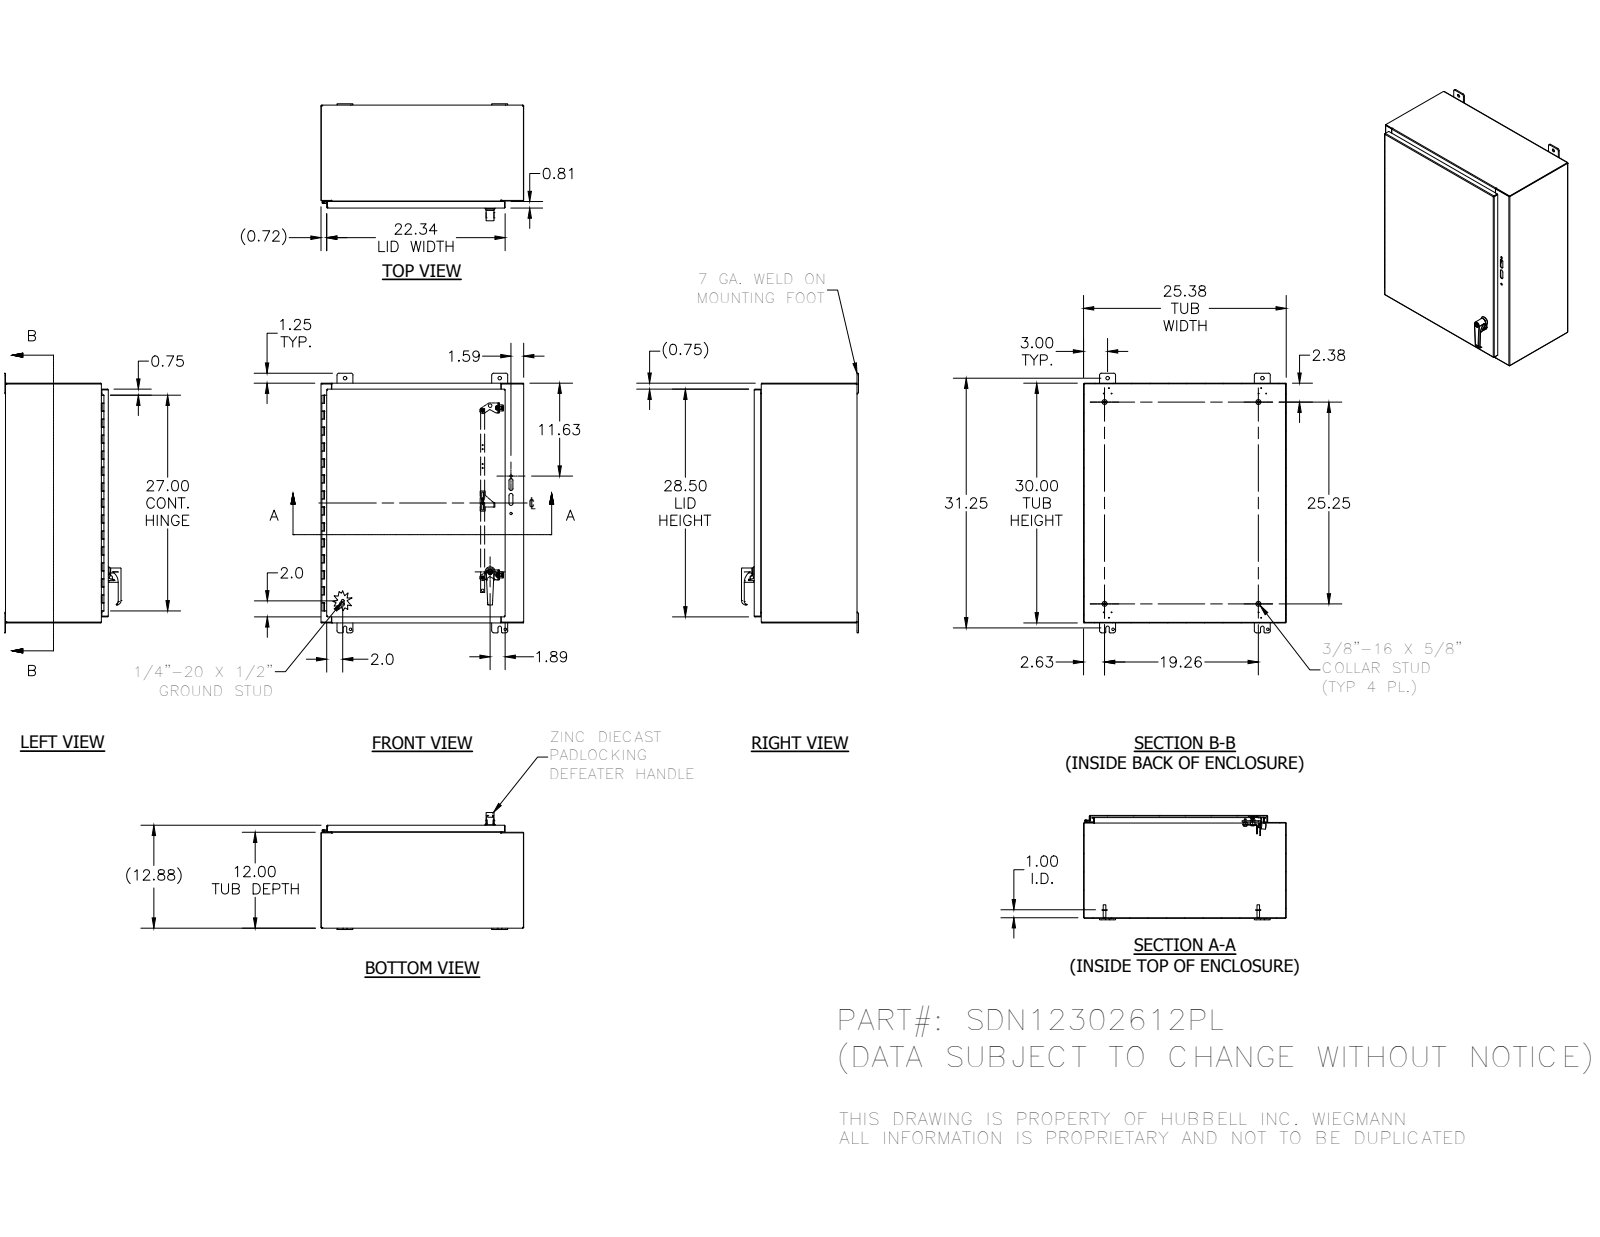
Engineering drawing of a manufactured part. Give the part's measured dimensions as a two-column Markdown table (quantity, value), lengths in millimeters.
| quantity | value |
| --- | --- |
| part name | SDN12302612PL; SDN12302612PLBKP; 388116; 34840 (+8 more) |
| STEP written by | Autodesk Inventor 2012 (AUTOMOTIVE_DESIGN) |
| units | millimeters |
| bodies | 49 solids, 1618 faces (836 planar, 557 cylindrical, 225 other) |
| overall size | 825.5 × 644.7 × 372.1 |
| volume | 3 918 000 mm³ |
| surface area | 4 123 000 mm² |
| round holes (diameter × count) | 3 × 12, 3.7 × 6, 8 × 4, 11.1 × 4, 8.1 × 3, 4 × 2, 5 × 2, 5.4 × 2, 5.6 × 2, 7.1 × 2, 8 × 2, 11.4 × 2 |
| round bosses / shafts (diameter × count) | 15.9 × 5, 8.4 × 5, 11.1 × 4, 7.6 × 4, 6.4 × 4, 5.7 × 4, 4.8 × 4, 19.1 × 2 |
| partial cylindrical surfaces (radius × count) | 0.5 × 38, 0.3 × 31, 6.4 × 22, 0.8 × 20, 2.7 × 20, 3.2 × 17, 0.6 × 16, 1.8 × 8 |
| main face-to-face distances | 1.9, 325.1, 642.8, 323.3, 327, 760.1, 640.9, 644.7, 302.9, 22.2 |
| hole center spacings | 530.9, 19.3, 40.5, 476.2, 492.3, 695.5, 712.9, 713 |
